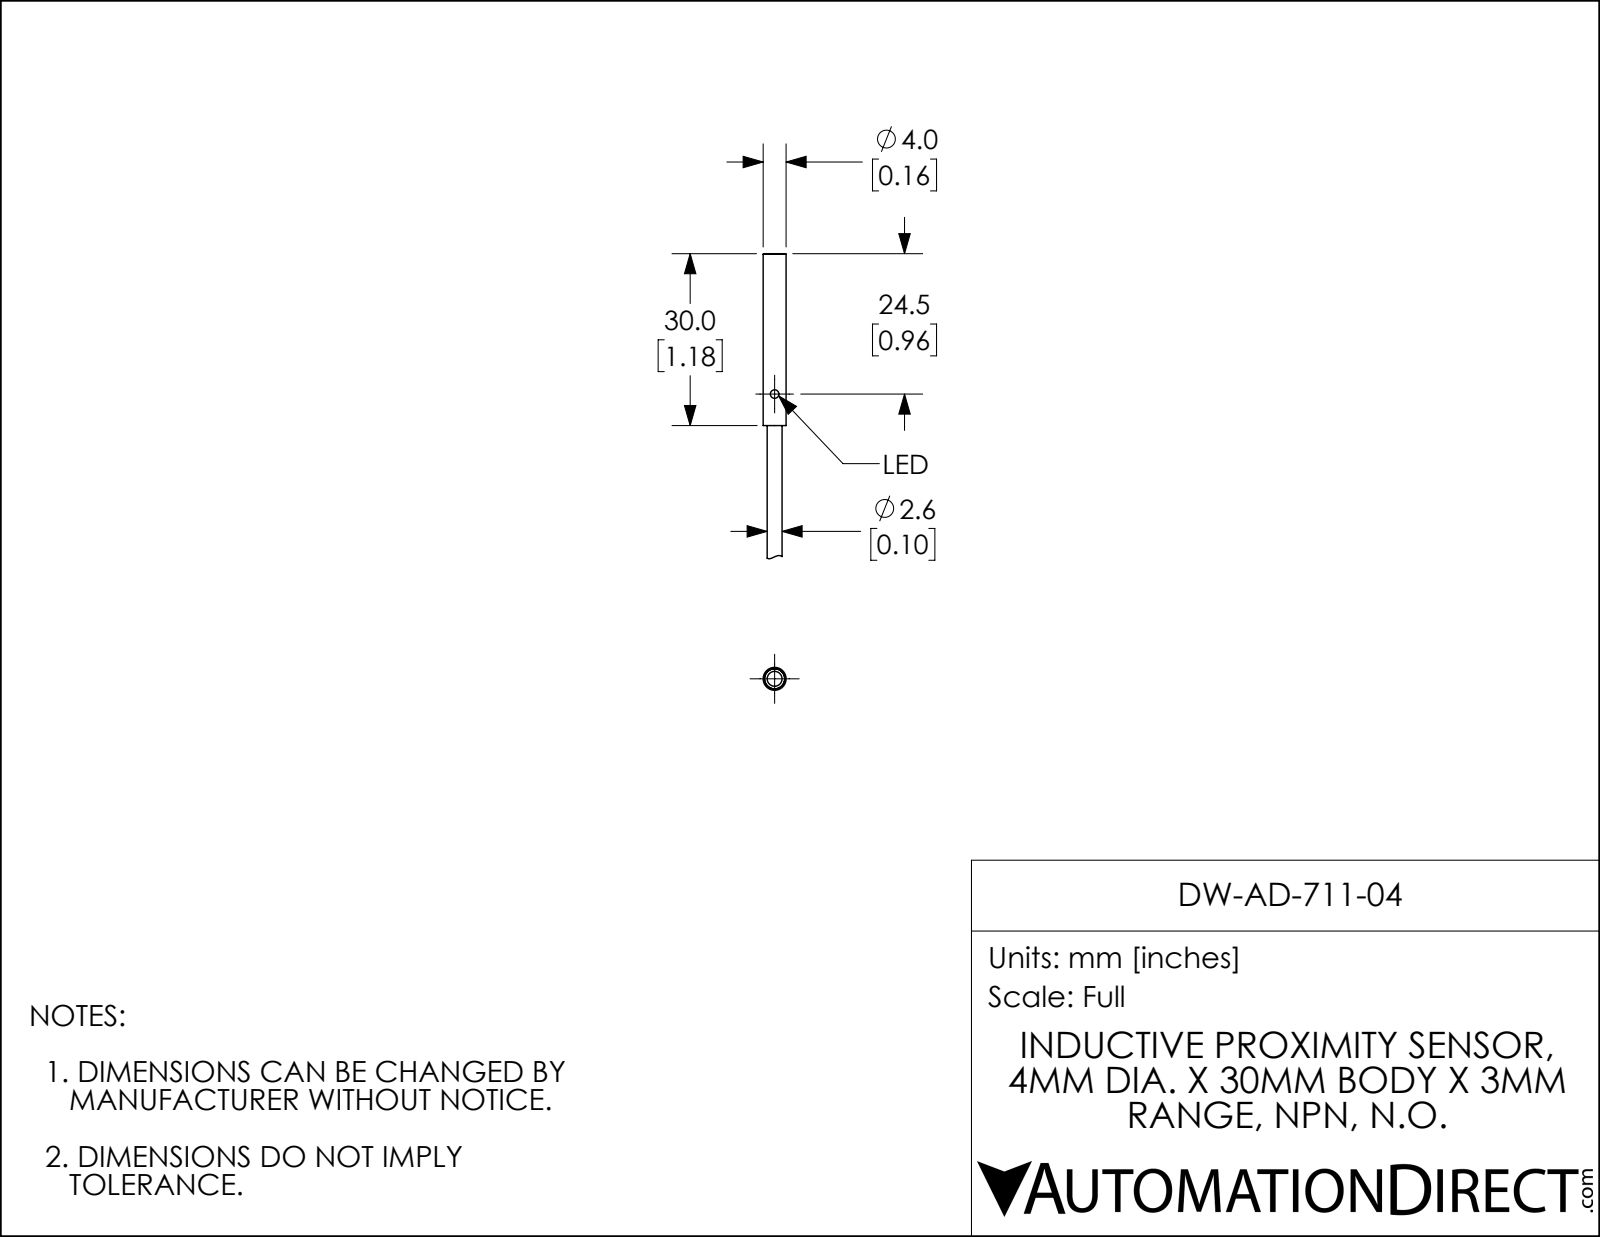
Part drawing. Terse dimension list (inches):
name: DW-AD-71x-04
written by: SolidWorks 2017 (AUTOMOTIVE_DESIGN)
unit: in
bodies: 2 solids, 10 faces (4 planar, 4 cylindrical, 2 other)
size: 2.103 × 0.157 × 0.157
volume: 0.021 in³; area: 1.632 in²
holes: 1× ⌀0.059, 1× ⌀0.14
bosses: 1× ⌀0.157, 1× ⌀0.138
face distances: 1.004, 0.994, 1.181, 1.171, 0.177
